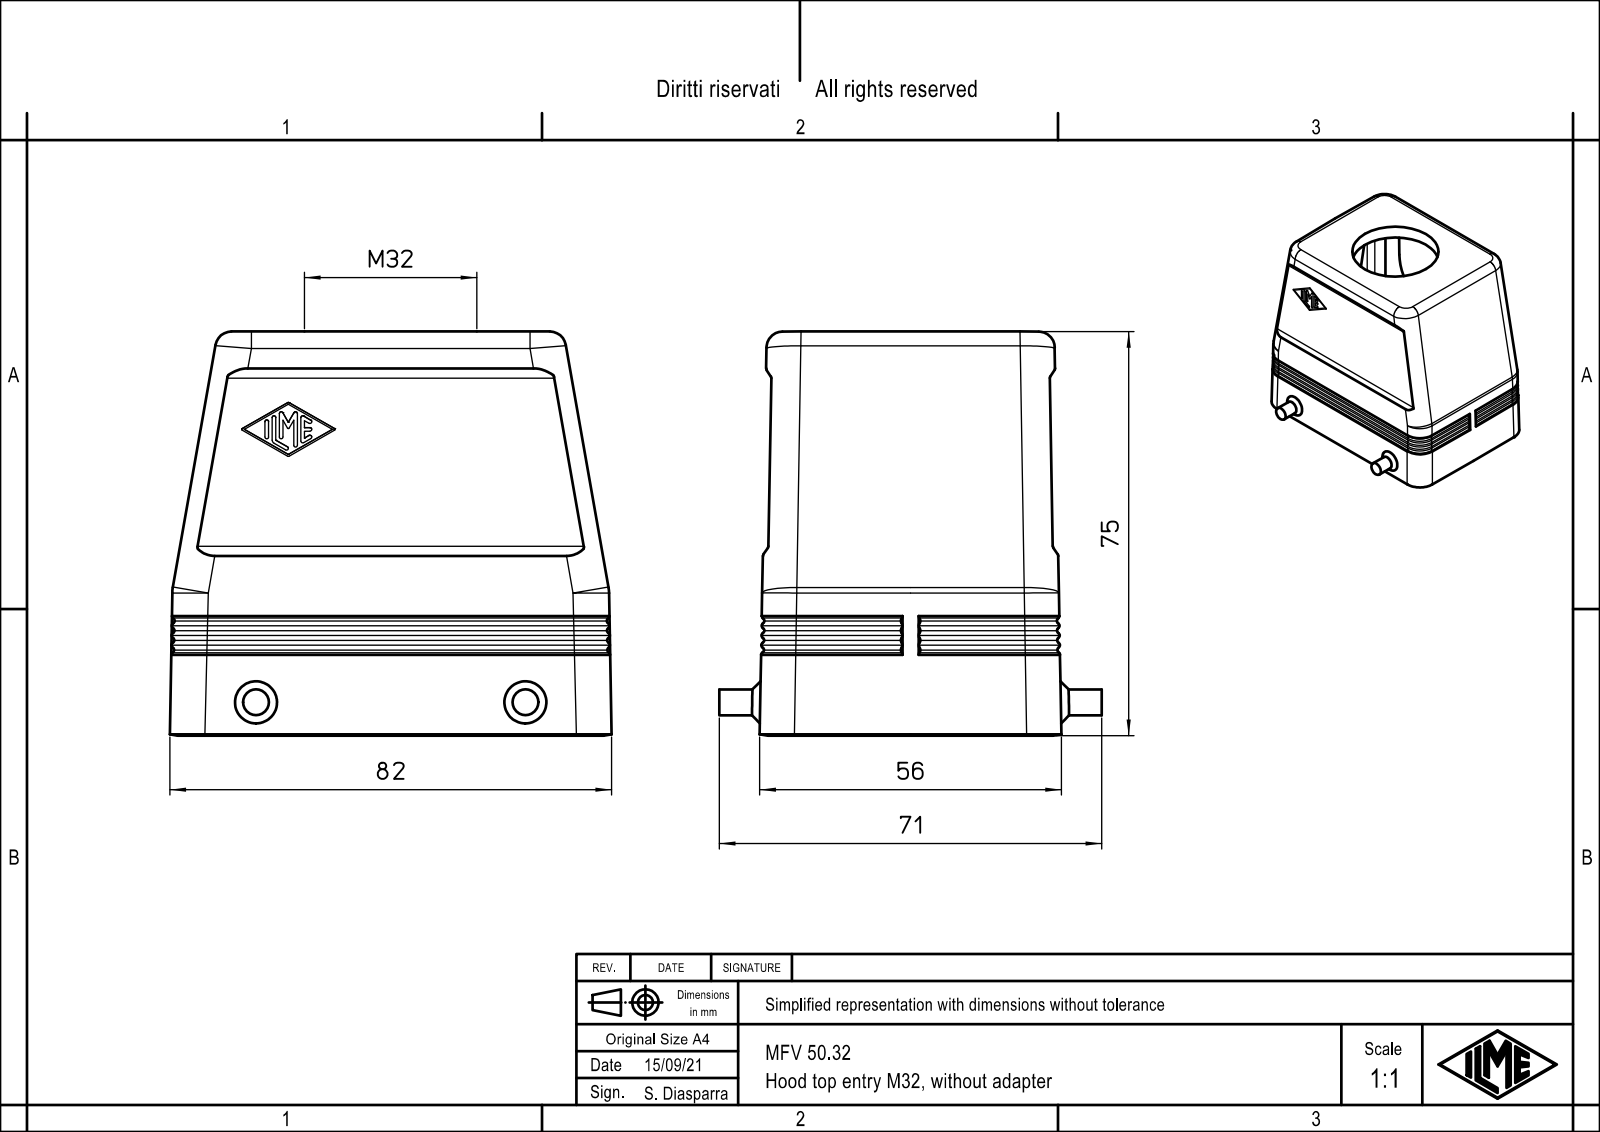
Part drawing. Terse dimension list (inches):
name: 23601_D
written by: Creo Elements/Direct Modeling 20.1B 02-Apr-2019 (C) Parametric Technology GmbH (AUTOMOTIVE_DESIGN)
unit: in
bodies: 1 solid, 438 faces (169 planar, 120 cylindrical, 149 other)
size: 3.228 × 2.953 × 2.795
volume: 5.716 in³; area: 67.44 in²
holes: 1× ⌀1.26
bosses: 2× ⌀0.189, 1× ⌀1.654
rounds: 44× R0.02, 13× R0.039, 10× R0.256, 8× R0.079, 4× R0.118, 4× R0.138, 1× R0.787
face distances: 0.039, 2.165, 2.126, 2.205, 0.307, 0.276, 0.275, 0.078, 2.953, 3.228
